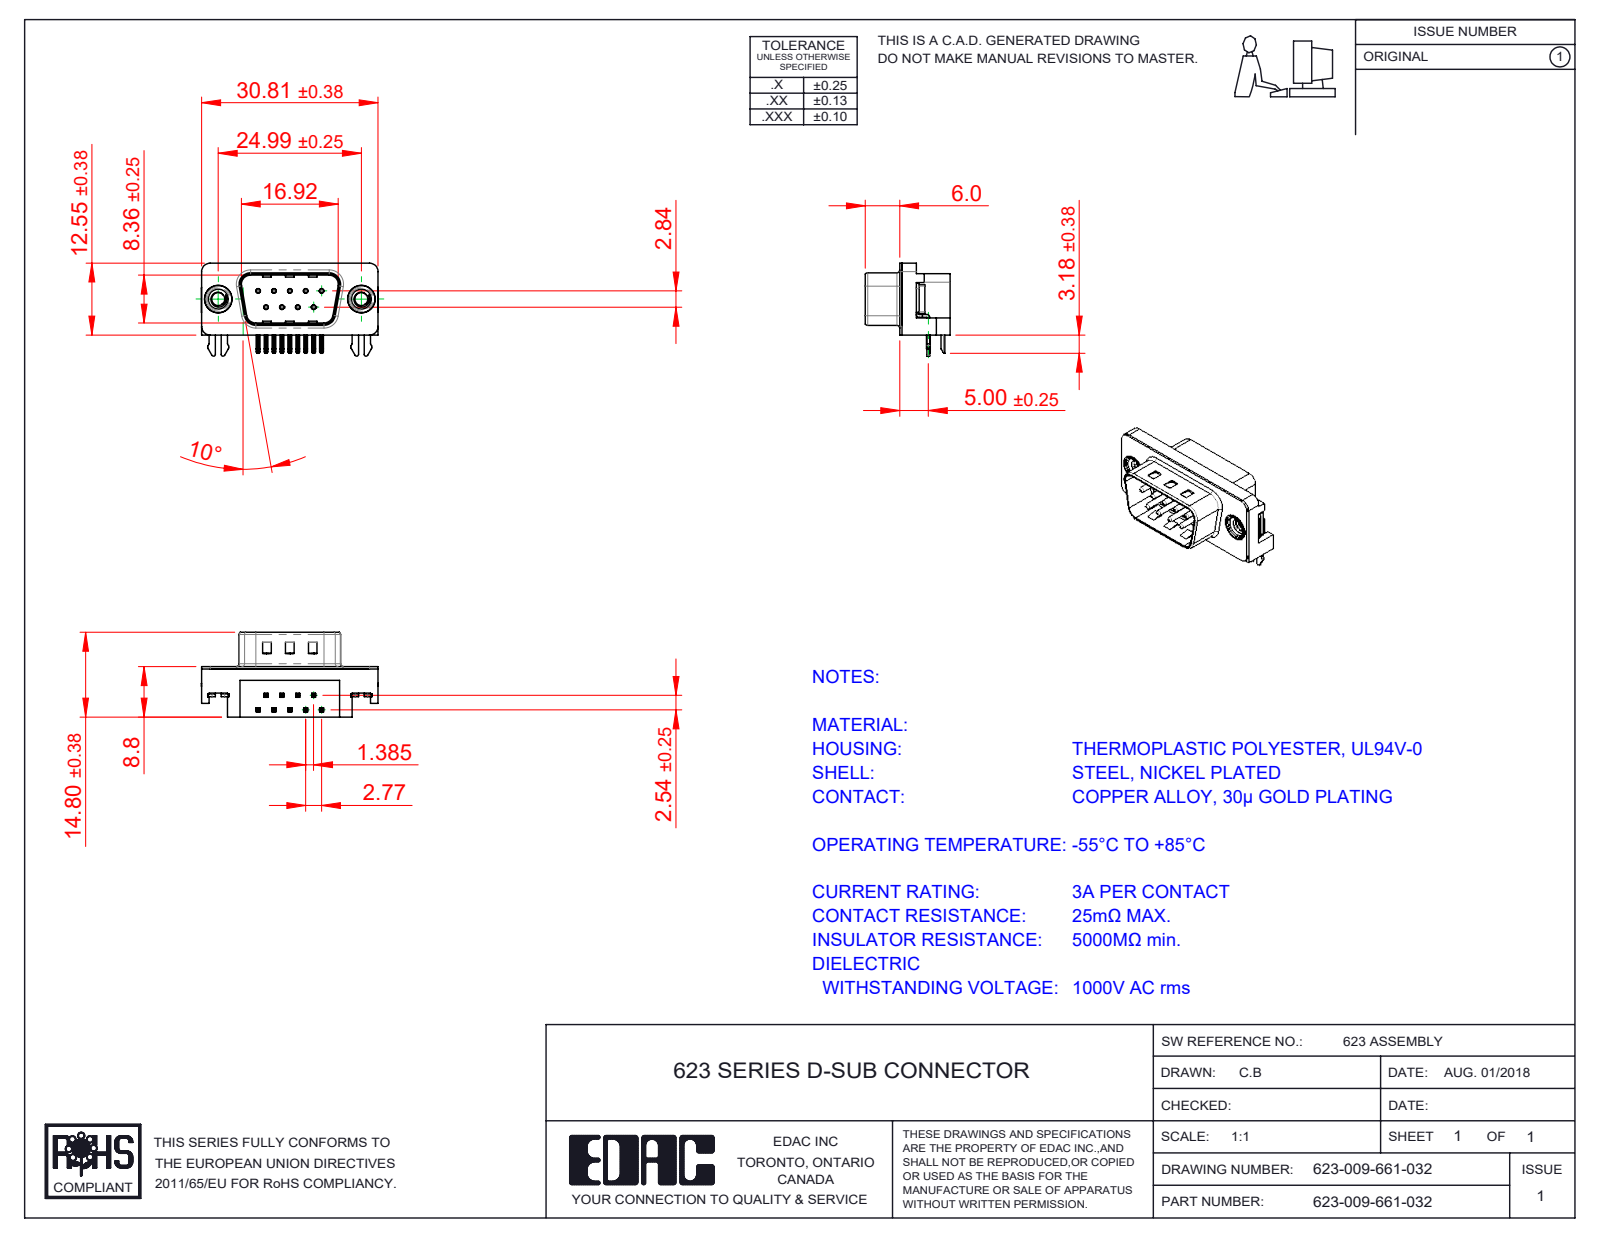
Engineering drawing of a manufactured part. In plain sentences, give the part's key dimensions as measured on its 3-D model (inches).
The part is named "623-009-661-032; 623 Contact Bottom; 623 Housing_9 Socket; 623 2 Prong Board Lock (+3 more)". Its 3-D file was written by "SolidWorks 2016 (CONFIG_CONTROL_DESIGN)". It is 15 solids with 1013 faces: 601 planar, 309 cylindrical and 103 other. Overall it measures 1.216 by 0.64 by 0.583 inches. Its volume is 0.151 cubic inches and its surface area 5.949 square inches. Round holes: 9 of diameter 0.014, 9 of diameter 0.031, 2 of diameter 0.089, 2 of diameter 0.157, 2 of diameter 0.189, 2 of diameter 0.197. Round bosses or shafts: 9 of diameter 0.03, 2 of diameter 0.193, 2 of diameter 0.187, 2 of diameter 0.154. Partial cylindrical surfaces (rounded edges, fillets, slot ends): 44 of radius 0.01, 18 of radius 0.005, 14 of radius 0.02, 8 of radius 0.039, 8 of radius 0.059, 4 of radius 0.013, 4 of radius 0.035, 4 of radius 0.063. The main face-to-face distances are 0.016, 0.331, 0.346, 0.232, 0.114, 0.098, 0.014, 0.345, 0.421, 0.407. The hole center spacings are 0.124, 0.109, 0.218, 0.198, 0.198, 0.327, 0.294, 0.295.
